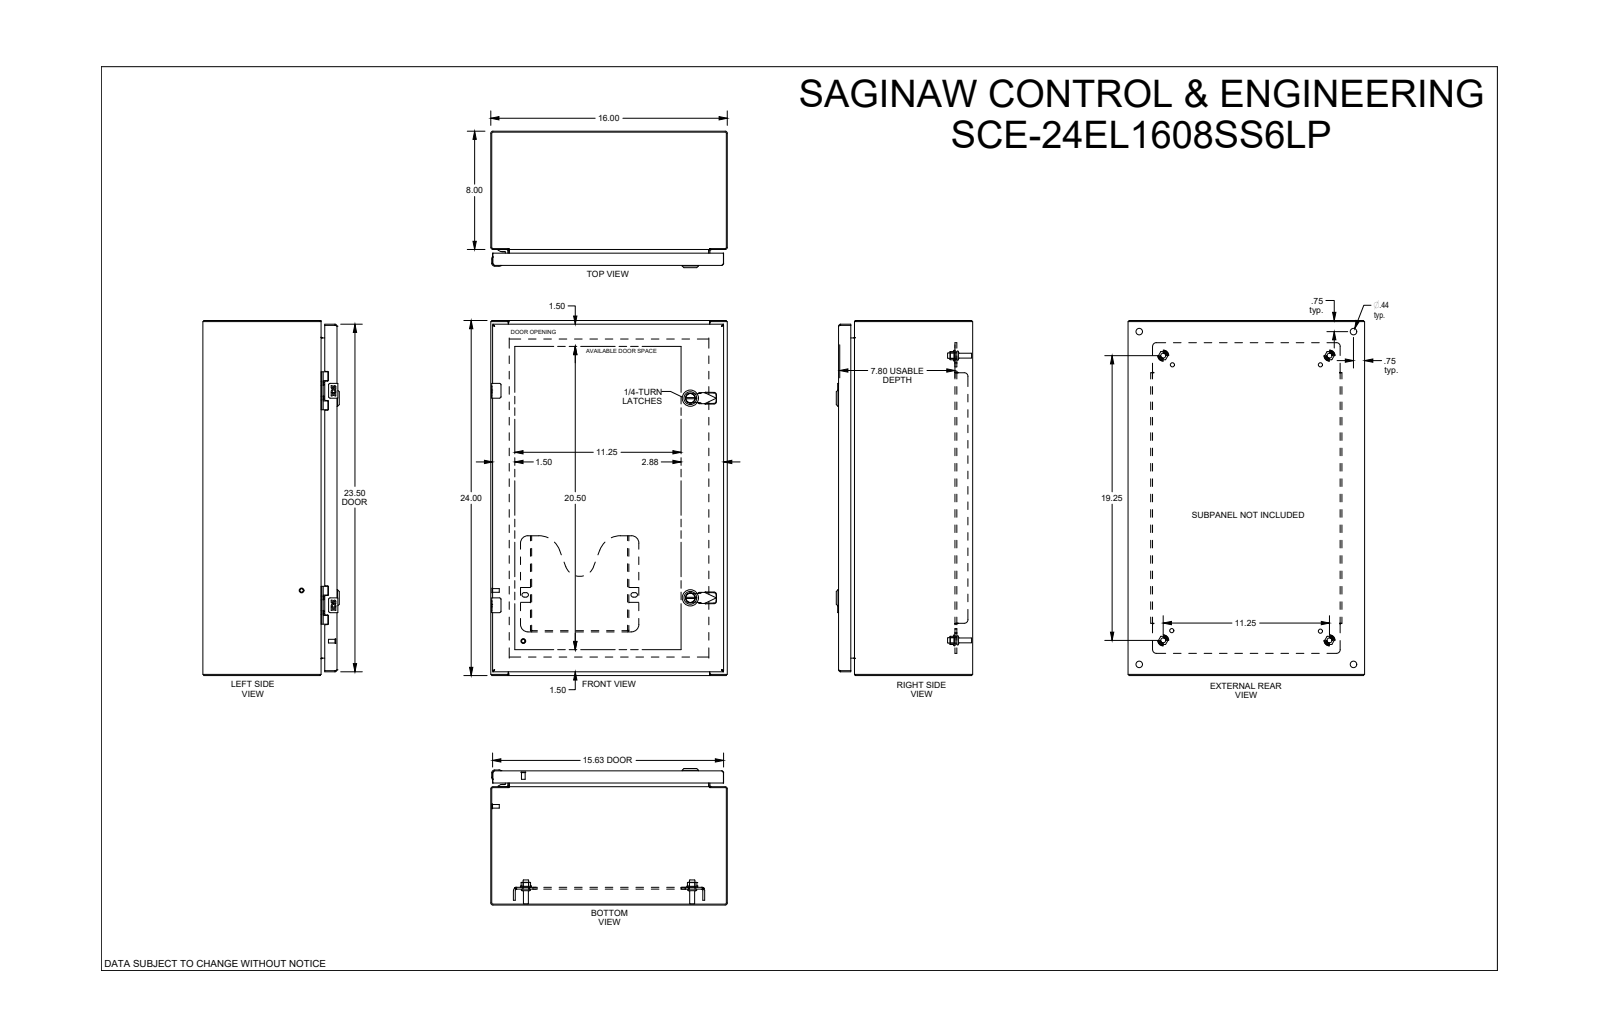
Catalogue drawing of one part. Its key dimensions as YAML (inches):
part_name: "SCE-24EL1608LP"
step_written_by: "SolidWorks 2021 (AUTOMOTIVE_DESIGN)"
units: inches
bodies: {solids: 45, faces: 2787, planar: 1089, cylindrical: 840, other: 858}
overall_size: [24, 16, 9.23]
volume: 168.8
surface_area: 4090
round_holes:
  - {diameter: 0.172, count: 4}
  - {diameter: 0.205, count: 4}
  - {diameter: 0.244, count: 4}
  - {diameter: 0.266, count: 4}
  - {diameter: 0.281, count: 4}
  - {diameter: 0.367, count: 4}
  - {diameter: 0.375, count: 4}
  - {diameter: 0.437, count: 4}
  - {diameter: 0.5, count: 4}
  - {diameter: 0.04, count: 2}
  - {diameter: 0.188, count: 2}
  - {diameter: 0.197, count: 2}
round_bosses_or_shafts:
  - {diameter: 0.17, count: 6}
  - {diameter: 0.366, count: 4}
  - {diameter: 0.332, count: 4}
  - {diameter: 0.25, count: 4}
  - {diameter: 0.248, count: 4}
  - {diameter: 0.24, count: 4}
  - {diameter: 0.196, count: 3}
  - {diameter: 1.102, count: 2}
partial_cylinders:
  - {radius: 0.012, count: 56}
  - {radius: 0.01, count: 28}
  - {radius: 0.015, count: 24}
  - {radius: 0.02, count: 20}
  - {radius: 0.04, count: 17}
  - {radius: 0.06, count: 13}
  - {radius: 0.029, count: 12}
  - {radius: 0.1, count: 12}
face_to_face_distances: [0.075, 0.06, 15.925, 9.073, 8.998, 9.013, 8.938, 1, 0.125, 1.2]
hole_center_spacings: [14.5, 0.985, 0.02, 0.493, 0.494, 2.298, 4.493, 12.978]
